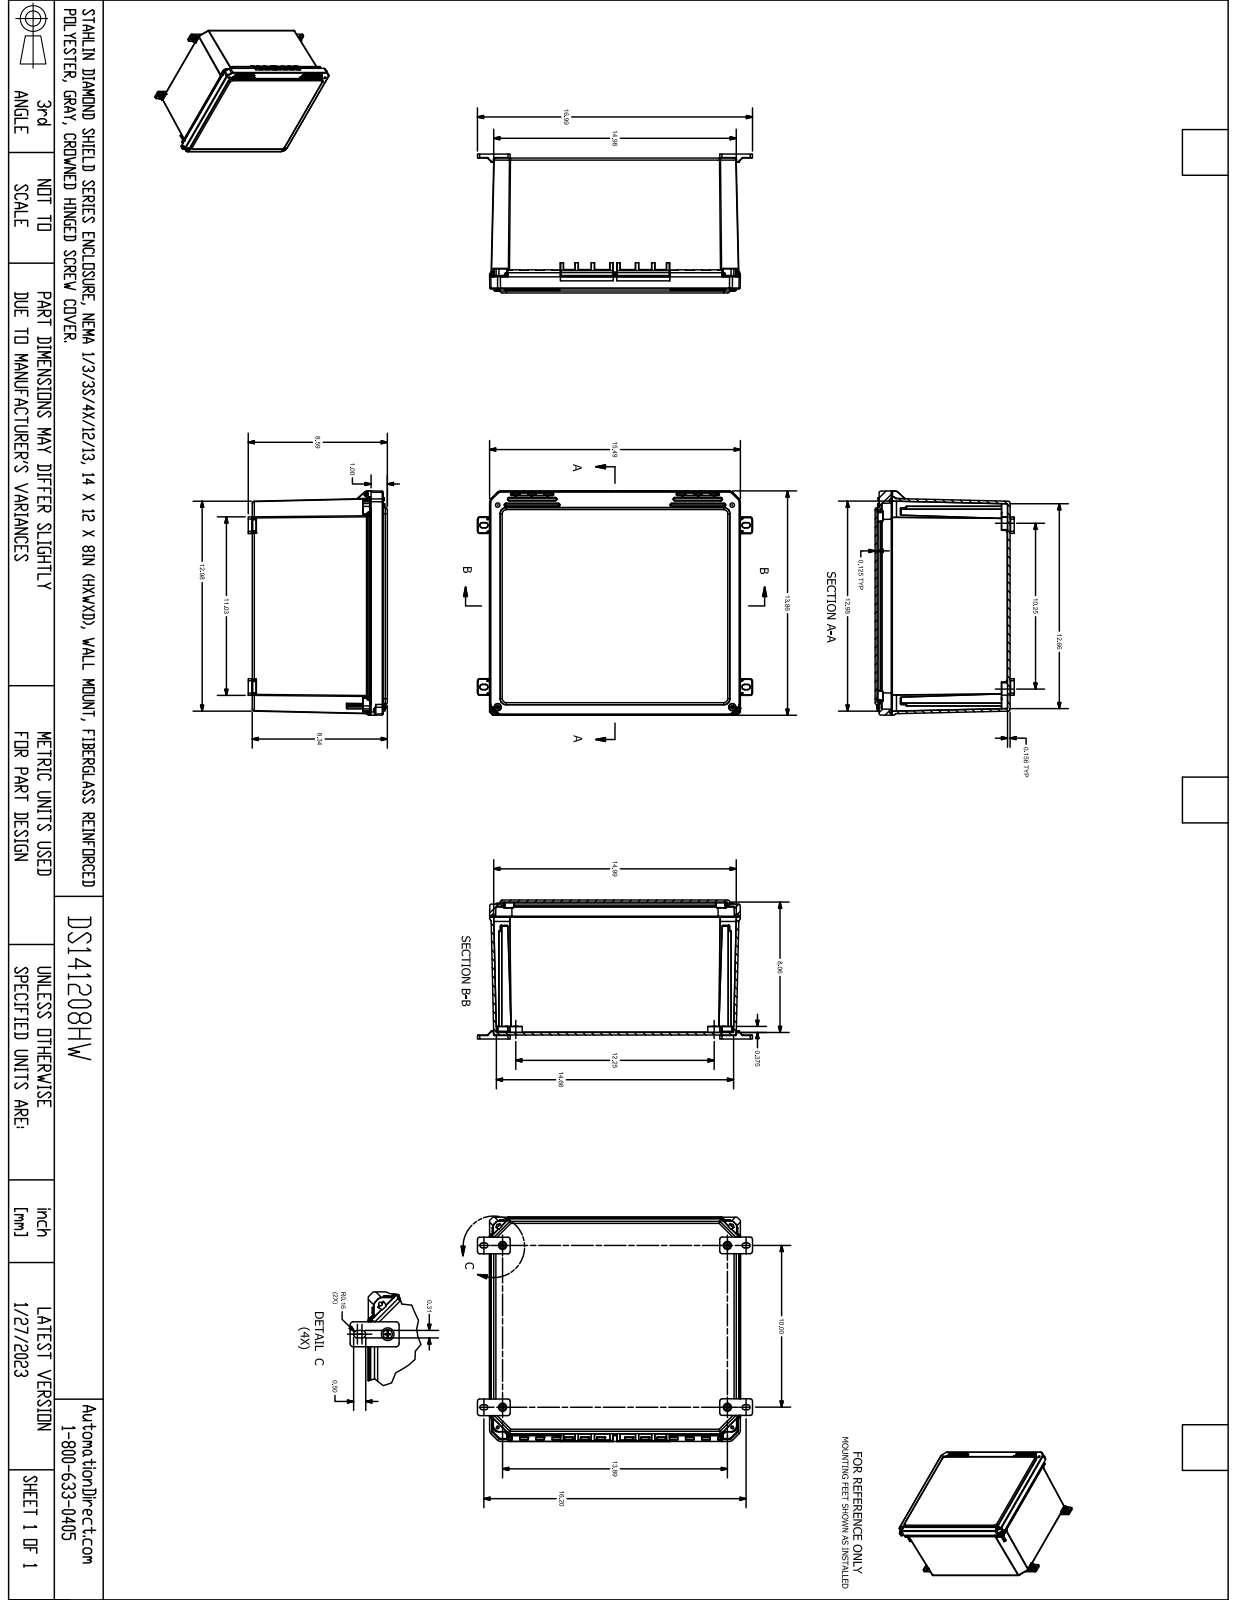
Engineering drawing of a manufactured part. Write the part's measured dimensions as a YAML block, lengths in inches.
part_name: "FR141208HW"
step_written_by: "SolidWorks 2021 (AUTOMOTIVE_DESIGN)"
units: inches
bodies: {solids: 23, faces: 2244, planar: 702, cylindrical: 889, other: 653}
overall_size: [15.493, 13.879, 8.767]
volume: 144.4
surface_area: 1820
round_holes:
  - {diameter: 0.152, count: 8}
  - {diameter: 0.159, count: 8}
  - {diameter: 0.156, count: 4}
  - {diameter: 0.252, count: 4}
  - {diameter: 0.253, count: 4}
  - {diameter: 0.137, count: 3}
  - {diameter: 0.15, count: 2}
  - {diameter: 0.219, count: 2}
  - {diameter: 0.227, count: 2}
  - {diameter: 0.313, count: 2}
round_bosses_or_shafts:
  - {diameter: 0.27, count: 8}
  - {diameter: 0.262, count: 4}
  - {diameter: 0.45, count: 2}
  - {diameter: 0.435, count: 2}
  - {diameter: 0.209, count: 2}
  - {diameter: 0.199, count: 2}
  - {diameter: 0.135, count: 2}
partial_cylinders:
  - {radius: 0.01, count: 186}
  - {radius: 0.005, count: 110}
  - {radius: 0.02, count: 54}
  - {radius: 0.03, count: 50}
  - {radius: 0.03, count: 24}
  - {radius: 0.09, count: 24}
  - {radius: 0.096, count: 24}
  - {radius: 0.062, count: 23}
face_to_face_distances: [0.156, 0.16, 8.183, 8.339, 0.125, 8.058, 8.213, 0.158, 0.159, 0.25]
hole_center_spacings: [13.417, 13.836, 14.243, 14.489, 17.55, 1.583, 10.25, 12.25]
